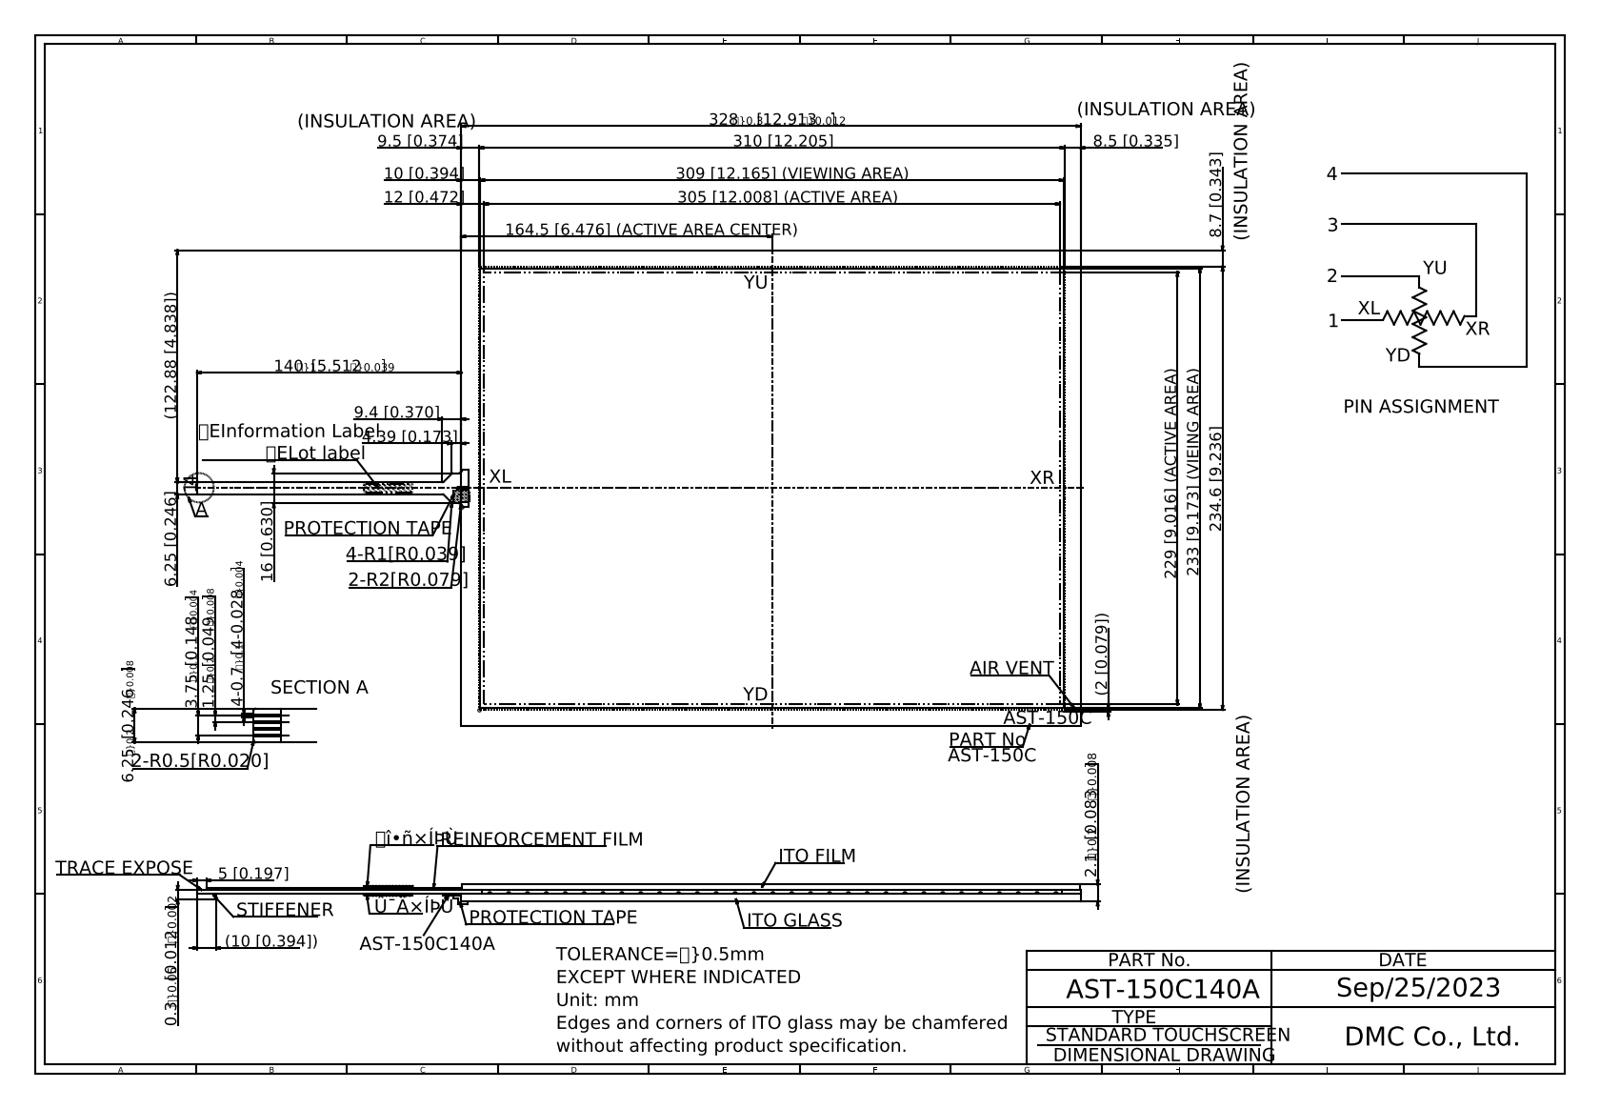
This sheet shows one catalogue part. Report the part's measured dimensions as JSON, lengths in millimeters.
{"part_name": "AST-150C140A", "step_written_by": "Autodesk Inventor 2020 (CONFIG_CONTROL_DESIGN)", "units": "millimeters", "bodies": {"solids": 1, "faces": 51, "planar": 45, "cylindrical": 6, "other": 0}, "overall_size": [468, 252, 2.1], "volume_mm3": 173472, "surface_area_mm2": 169882, "partial_cylinders_radius": [[1, 4], [0.5, 2]], "face_to_face_distances": [2.1, 2, 1.9, 1.8, 252, 328, 1.5, 0.4, 0.5, 0.6]}
